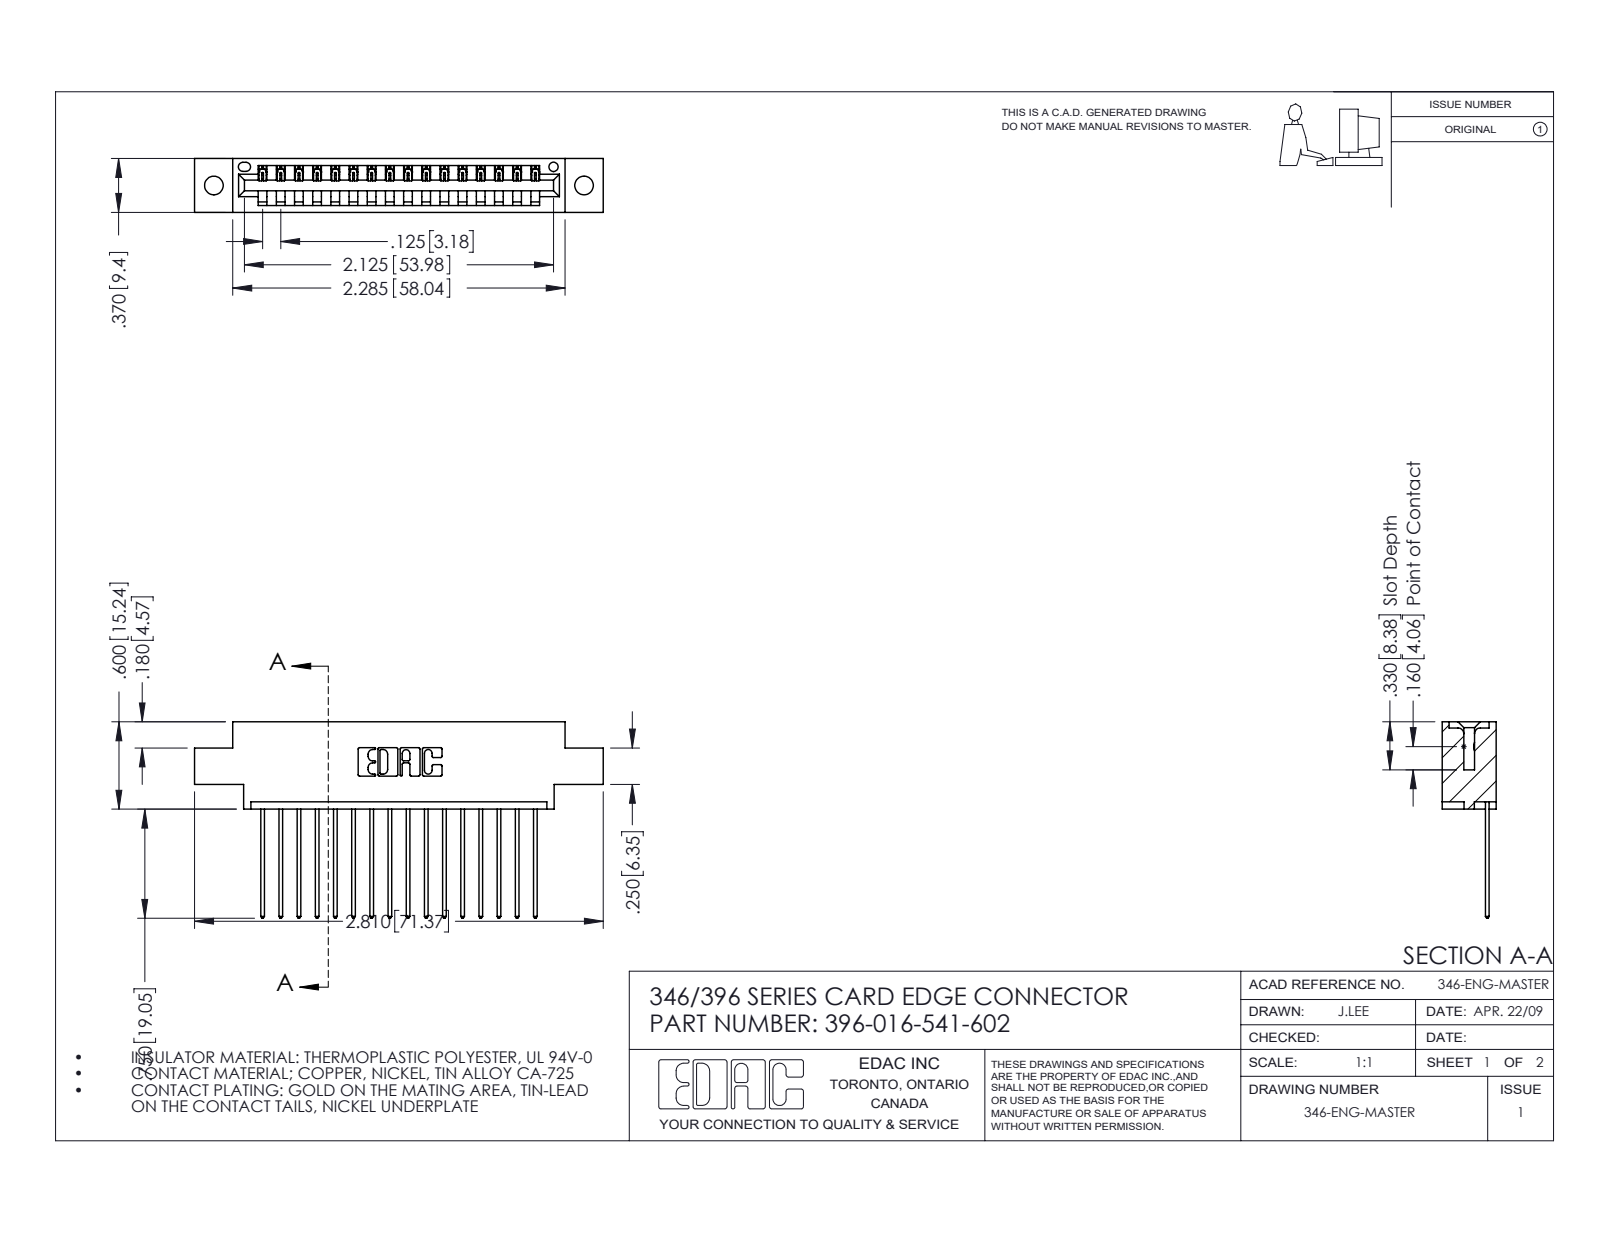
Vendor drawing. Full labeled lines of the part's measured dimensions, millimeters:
Part name (STEP PRODUCT): 345-292-001_345-293-141; 346 Part_0.170 Offset - 0.128 Dia; 396-016-541-602
STEP written by: SolidWorks 2016 (CONFIG_CONTROL_DESIGN)
Units: millimetres
Bodies: 17 solids, 1054 faces (720 planar, 334 cylindrical, 0 other)
Overall size (bounding box): 71.4 × 34.3 × 9.4
Volume: 6 520 mm³ · Surface area: 8 065 mm²
Round holes (diameter × count): ⌀3.3 ×2, ⌀1.6 ×1
Partial cylindrical surfaces — rounded edges, fillets, slot ends (radius × count): R0.2 ×32, R0.3 ×32, R0.3 ×22, R0.2 ×6, R0.8 ×6, R0.7 ×3, R0.8 ×2, R1 ×2
Main face-to-face distances: 1.2, 8.2, 9.4, 6.4, 1.8, 7.6, 0.6, 3.8, 5.6, 2.5
Hole centre spacings: 6.2, 59.4, 64.6
